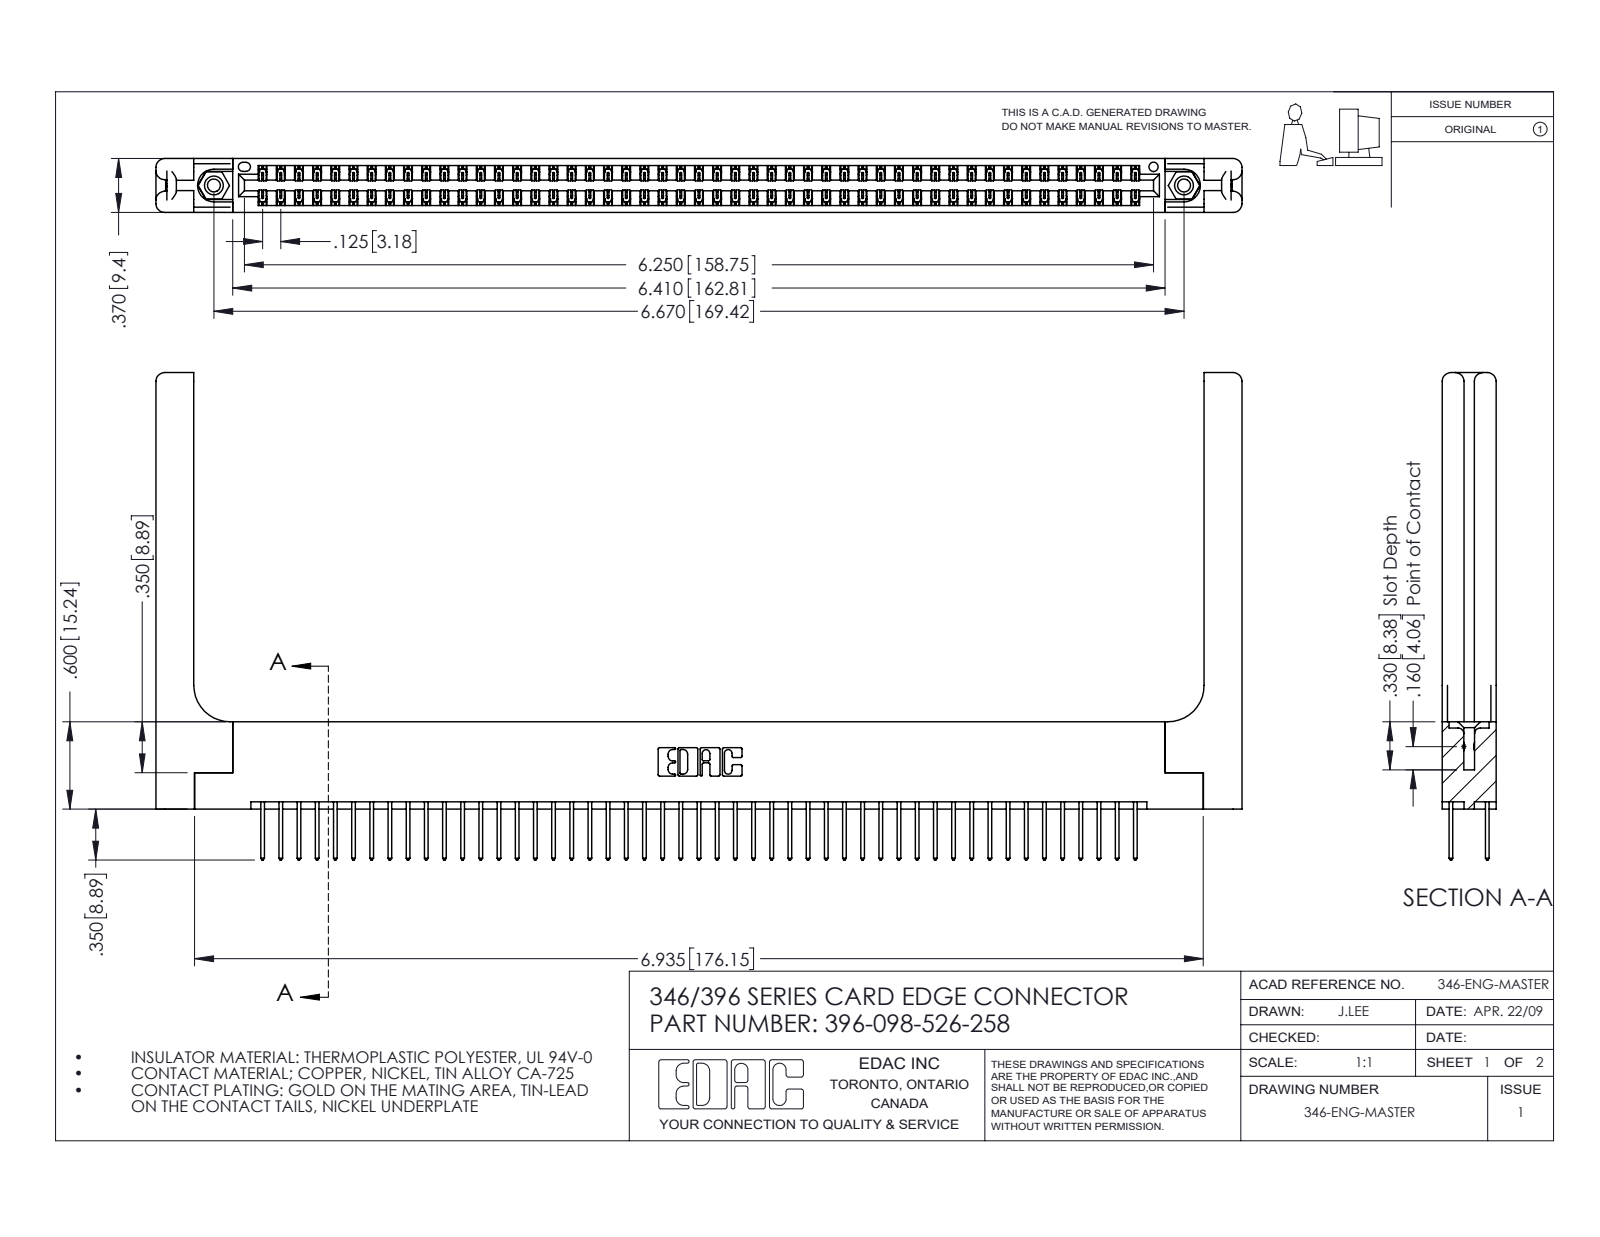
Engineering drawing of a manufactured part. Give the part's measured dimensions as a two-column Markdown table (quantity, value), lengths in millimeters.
| quantity | value |
| --- | --- |
| part name | 396-098-526-258; 346 Part_Flush Mounting Lugs - 0.156 Dia-TH; 346-220-058_345-220-058; 345-250-001_345-250-001-102 (+1 more) |
| STEP written by | SolidWorks 2016 (CONFIG_CONTROL_DESIGN) |
| units | millimeters |
| bodies | 103 solids, 5474 faces (3654 planar, 1760 cylindrical, 60 other) |
| overall size | 189.6 × 85.1 × 9.4 |
| volume | 26 200 mm³ |
| surface area | 31 520 mm² |
| round holes (diameter × count) | 2.3 × 2, 3.2 × 2, 4 × 2, 1.6 × 1 |
| round bosses / shafts (diameter × count) | 3.9 × 2 |
| partial cylindrical surfaces (radius × count) | 0.2 × 147, 0.3 × 98, 0.3 × 22, 1.5 × 16, 0.2 × 6, 0.8 × 6, 0.7 × 3, 0.4 × 2 |
| main face-to-face distances | 1.2, 8.2, 9.4, 1.8, 6.4, 0.6, 7.6, 3.8, 3.8, 7 |
| hole center spacings | 6.2, 164.1, 169.4 |
